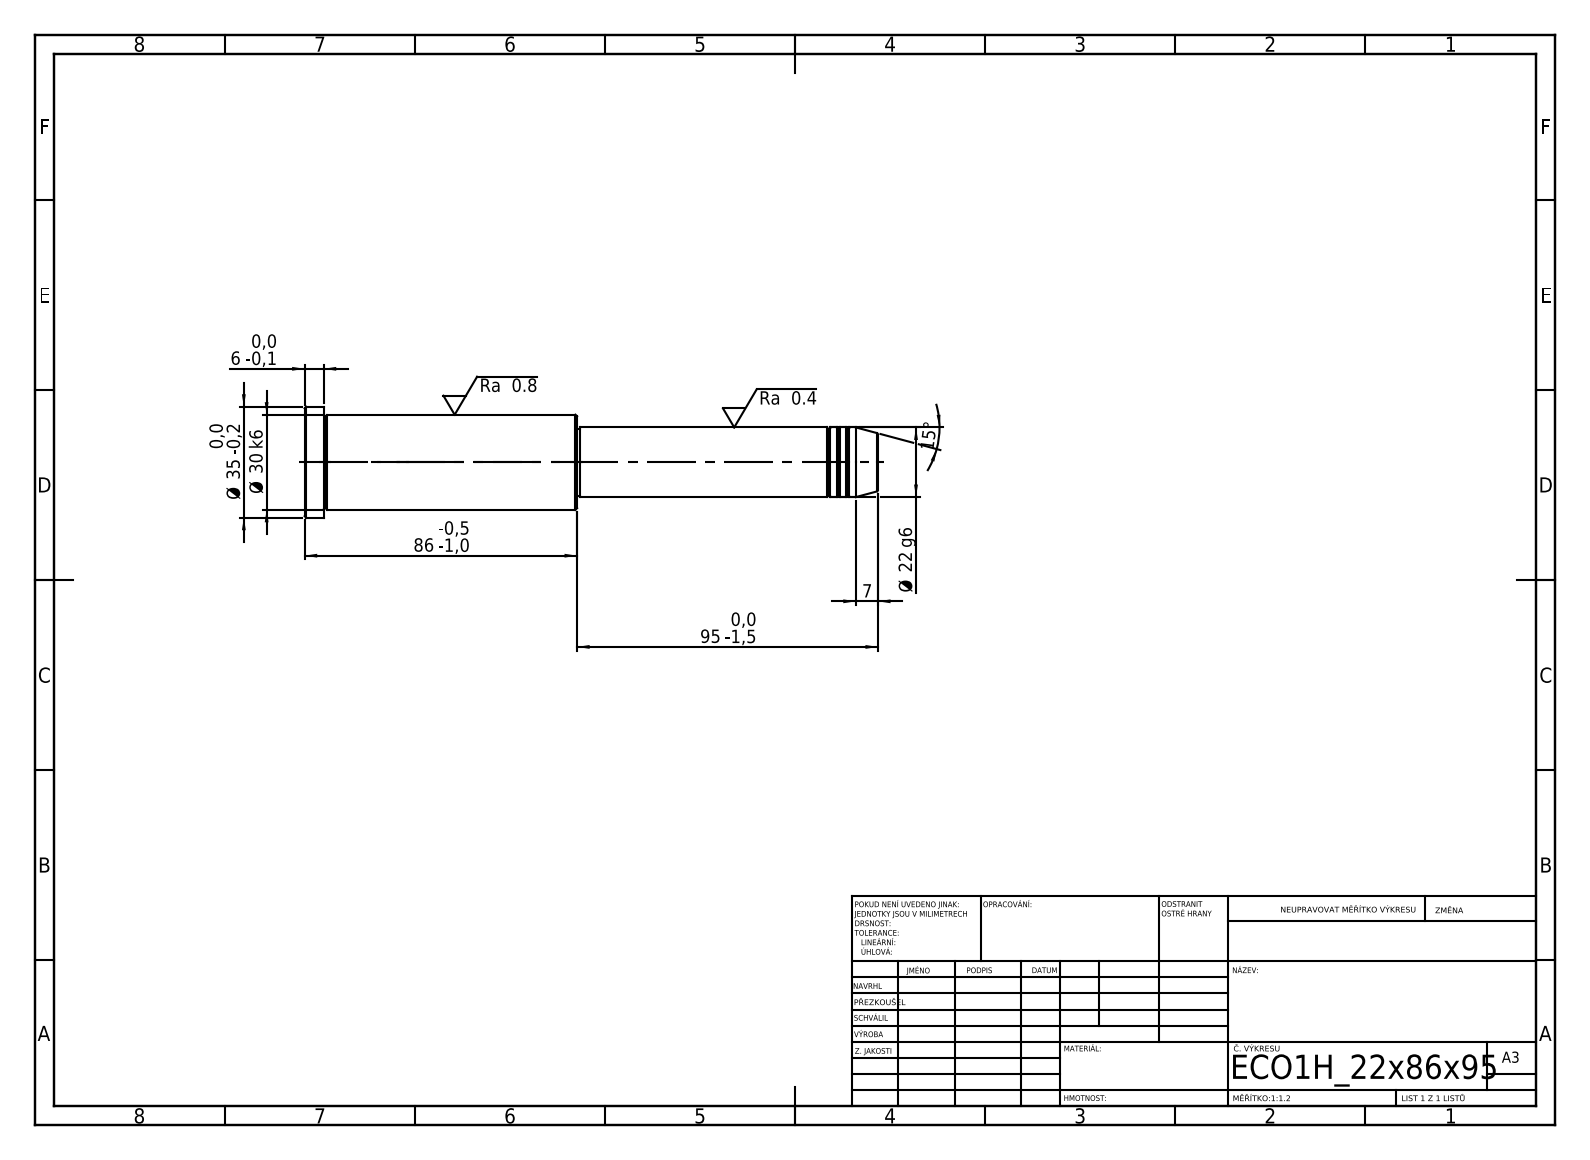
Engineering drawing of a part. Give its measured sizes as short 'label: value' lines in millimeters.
written by: SolidWorks 2019 (CONFIG_CONTROL_DESIGN)
unit: mm
bodies: 1 solid, 43 faces (5 planar, 14 cylindrical, 24 other)
size: 181 × 35 × 35
volume: 97 829 mm³; area: 16 702 mm²
bosses: 1× ⌀35, 1× ⌀30, 1× ⌀22, 1× ⌀21
face distances: 86, 80, 6, 95, 175, 181, 94, 1, 81, 87
